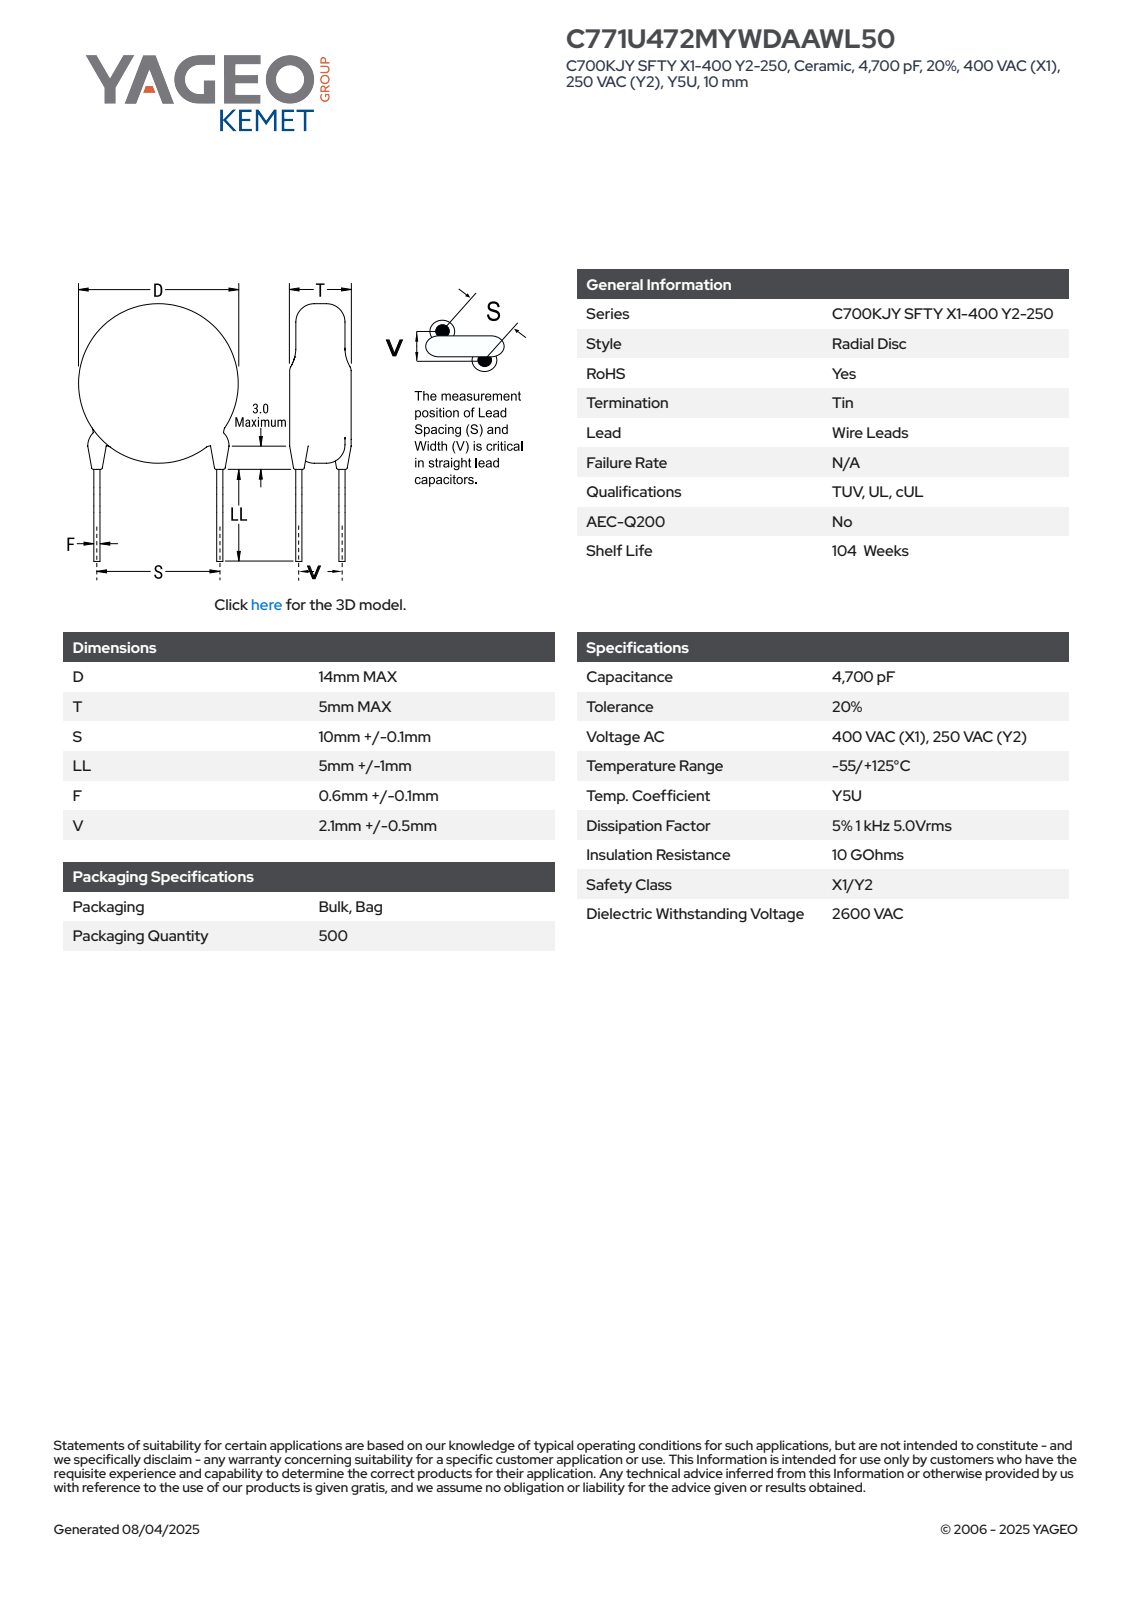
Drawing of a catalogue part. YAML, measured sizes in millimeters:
part_name: "CCD_KST_14X5_D14T5S10.1LL6F0.7V2.1"
step_written_by: "SolidWorks 2021 (AUTOMOTIVE_DESIGN)"
units: millimeters
bodies: {solids: 4, faces: 77, planar: 63, cylindrical: 10, other: 4}
overall_size: [20.38, 14, 5]
volume: 762
surface_area: 550
round_bosses_or_shafts:
  - {diameter: 1.2, count: 2}
  - {diameter: 0.7, count: 2}
  - {diameter: 14, count: 1}
face_to_face_distances: [5, 5.99, 14.57, 8.58, 12.92, 6.93, 1.65, 0.45, 6.74, 0.32]
